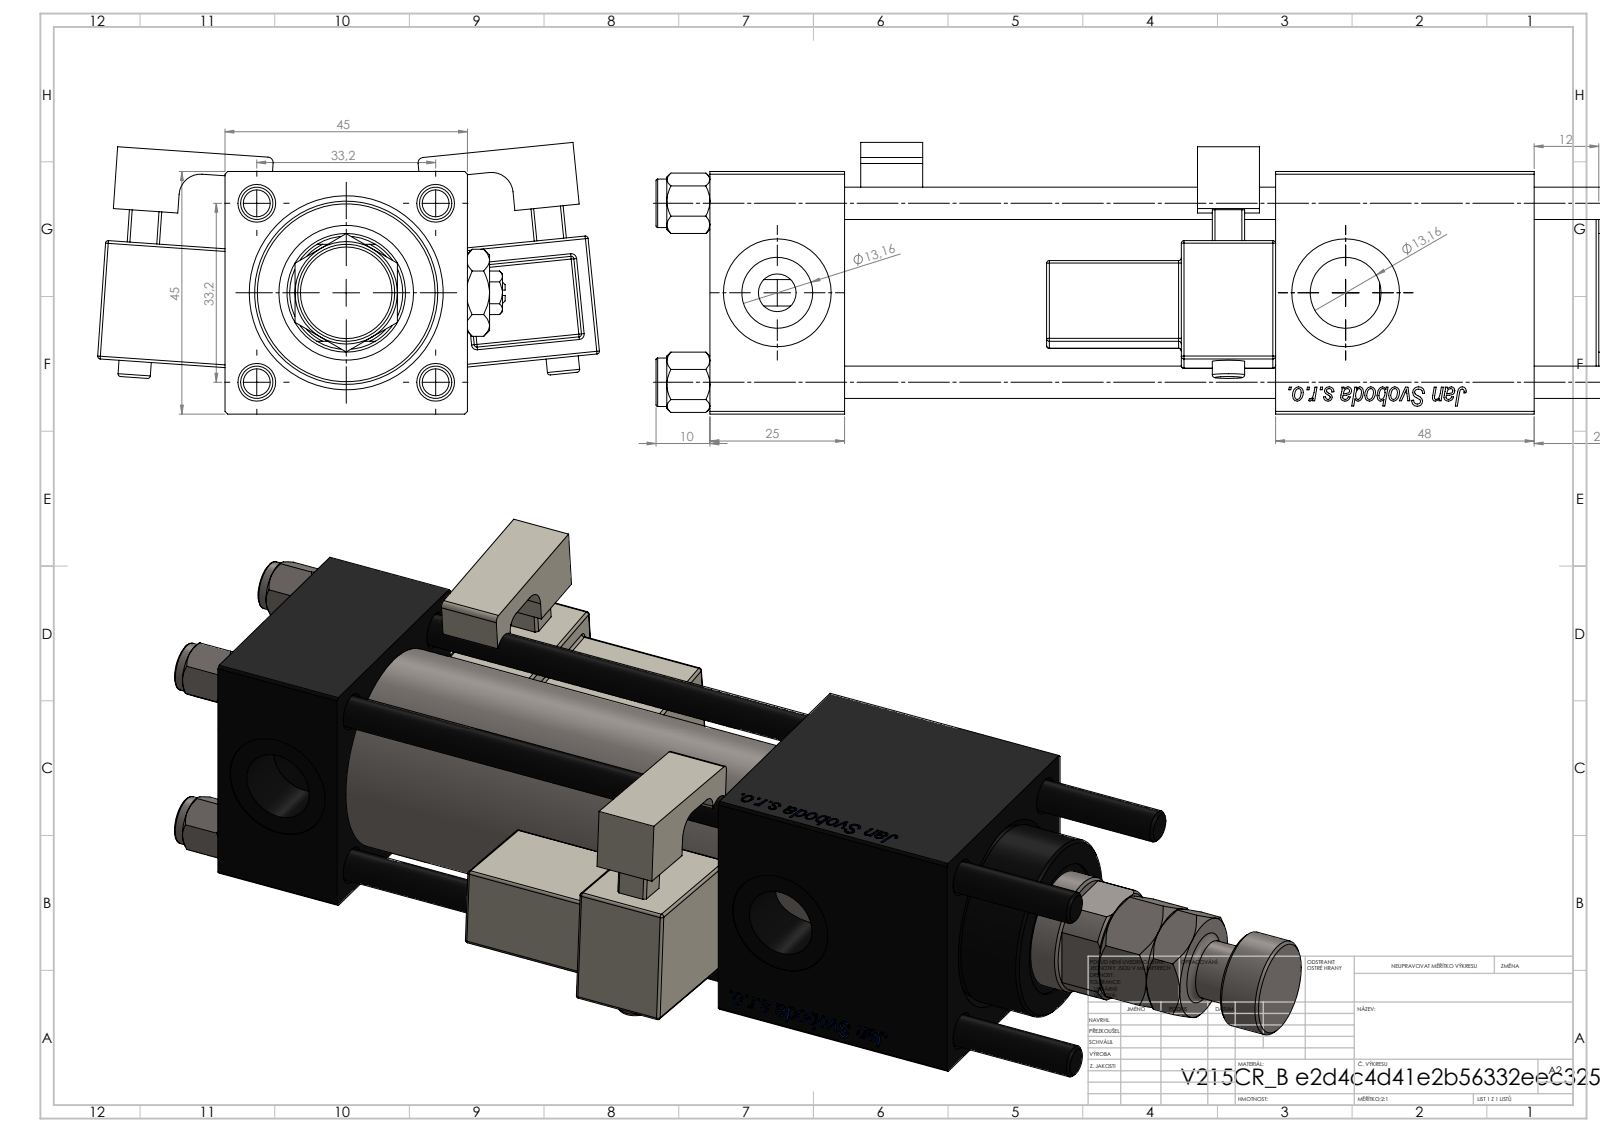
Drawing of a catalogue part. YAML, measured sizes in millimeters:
part_name: "MFA; V215CR_B_TYCINKA; Zatka_pro_OIL_PORT; NUT_M5_B (+4 more)"
step_written_by: "SolidWorks 2019 (CONFIG_CONTROL_DESIGN)"
units: millimeters
bodies: {solids: 16, faces: 1466, planar: 556, cylindrical: 152, other: 758}
overall_size: [221, 93.14, 50.4]
volume: 286199
surface_area: 104260
round_holes:
  - {diameter: 6, count: 4}
  - {diameter: 7, count: 2}
  - {diameter: 13.16, count: 2}
  - {diameter: 20, count: 2}
  - {diameter: 10.5, count: 1}
  - {diameter: 22, count: 1}
  - {diameter: 24, count: 1}
  - {diameter: 25, count: 1}
  - {diameter: 32, count: 1}
  - {diameter: 33, count: 1}
round_bosses_or_shafts:
  - {diameter: 9, count: 4}
  - {diameter: 6, count: 2}
  - {diameter: 38, count: 1}
  - {diameter: 34, count: 1}
  - {diameter: 18, count: 1}
  - {diameter: 11, count: 1}
partial_cylinders:
  - {radius: 0.5, count: 48}
  - {radius: 1, count: 2}
  - {radius: 2.5, count: 2}
  - {radius: 4, count: 2}
  - {radius: 10.5, count: 1}
face_to_face_distances: [45, 25, 105, 80, 62.5, 153, 3, 48, 20, 17.5]
hole_center_spacings: [23.48, 33.2, 46.95, 105.5]
